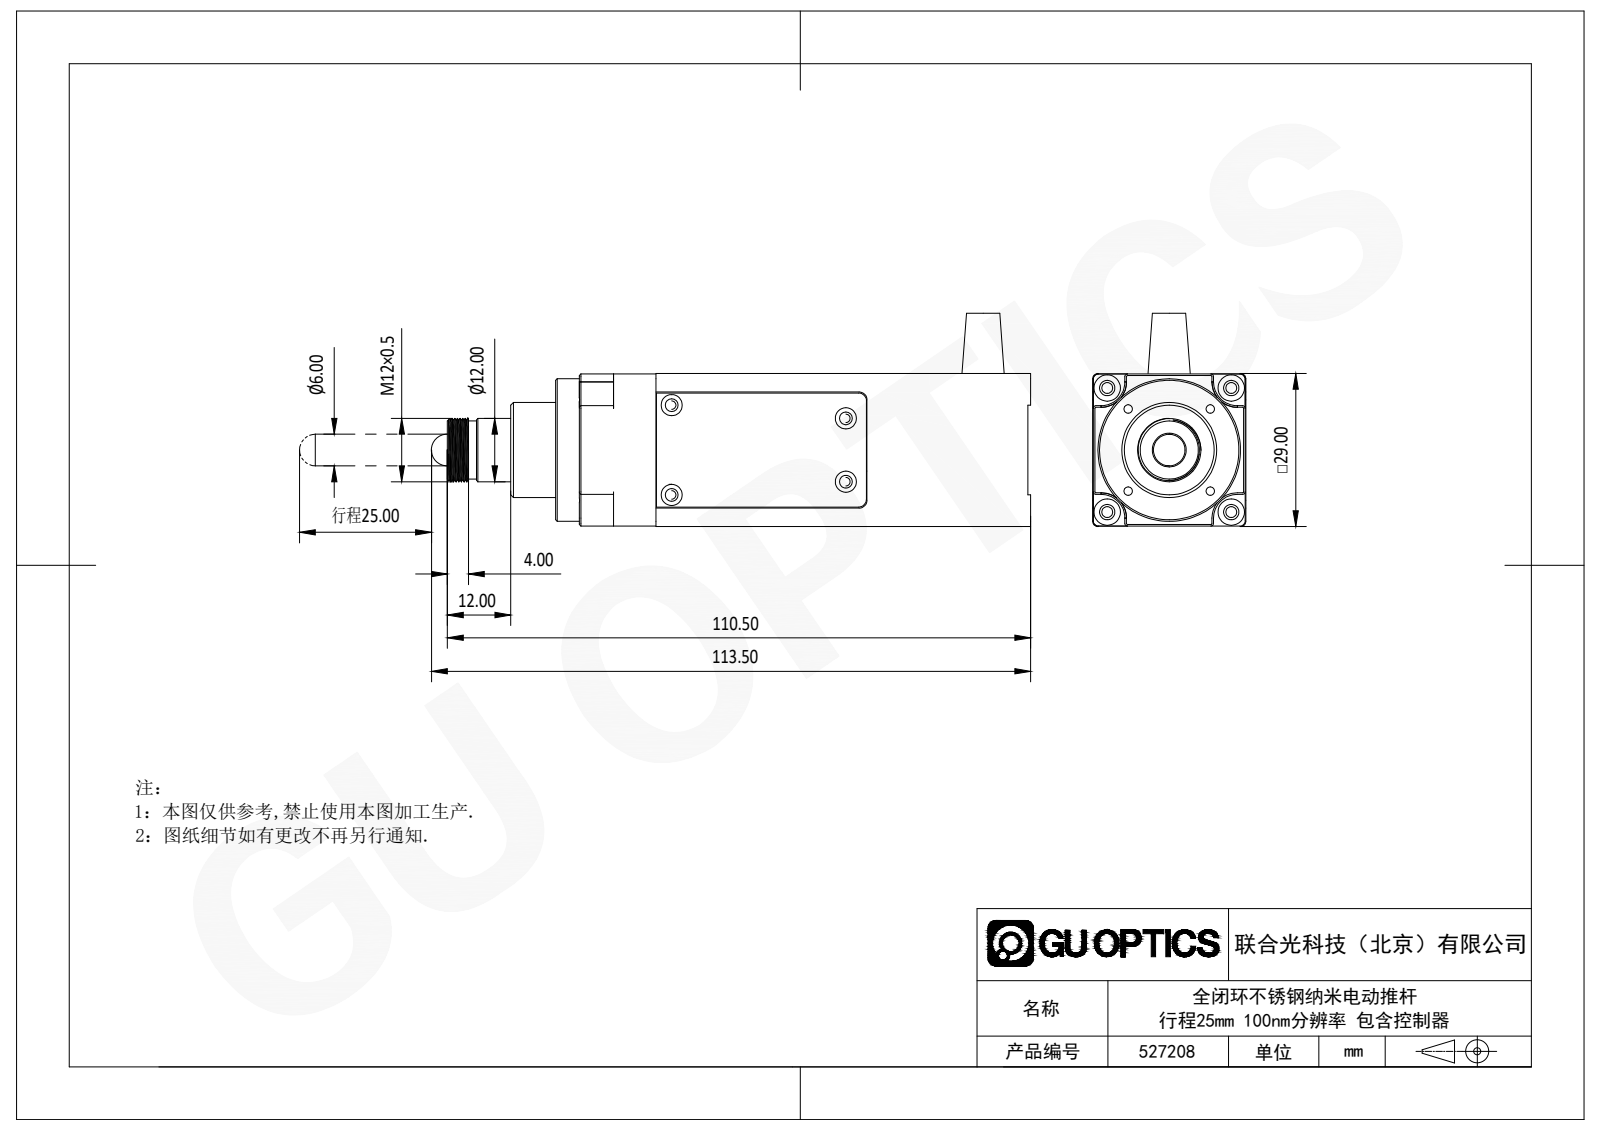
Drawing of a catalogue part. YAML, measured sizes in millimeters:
part_name: "527208"
step_written_by: "SolidWorks 2020 (CONFIG_CONTROL_DESIGN)"
units: millimeters
bodies: {solids: 0, faces: 379, planar: 136, cylindrical: 183, other: 60}
overall_size: [113.5, 40.4, 29]
round_holes:
  - {diameter: 5, count: 4}
  - {diameter: 1, count: 1}
  - {diameter: 11, count: 1}
  - {diameter: 12, count: 1}
  - {diameter: 18, count: 1}
  - {diameter: 27, count: 1}
round_bosses_or_shafts:
  - {diameter: 1.6, count: 12}
  - {diameter: 2.5, count: 10}
  - {diameter: 4, count: 8}
  - {diameter: 2.4, count: 8}
  - {diameter: 5, count: 4}
  - {diameter: 6.4, count: 1}
  - {diameter: 6, count: 1}
partial_cylinders:
  - {radius: 1.5, count: 10}
  - {radius: 0.5, count: 8}
  - {radius: 1, count: 8}
  - {radius: 2, count: 4}
  - {radius: 4.5, count: 4}
face_to_face_distances: [28.9, 29, 28.8, 27.5, 1.5, 27.4, 1.4, 70.5, 4.5, 6]
hole_center_spacings: [25.32, 26.78, 50.06, 52.06, 12, 17]
